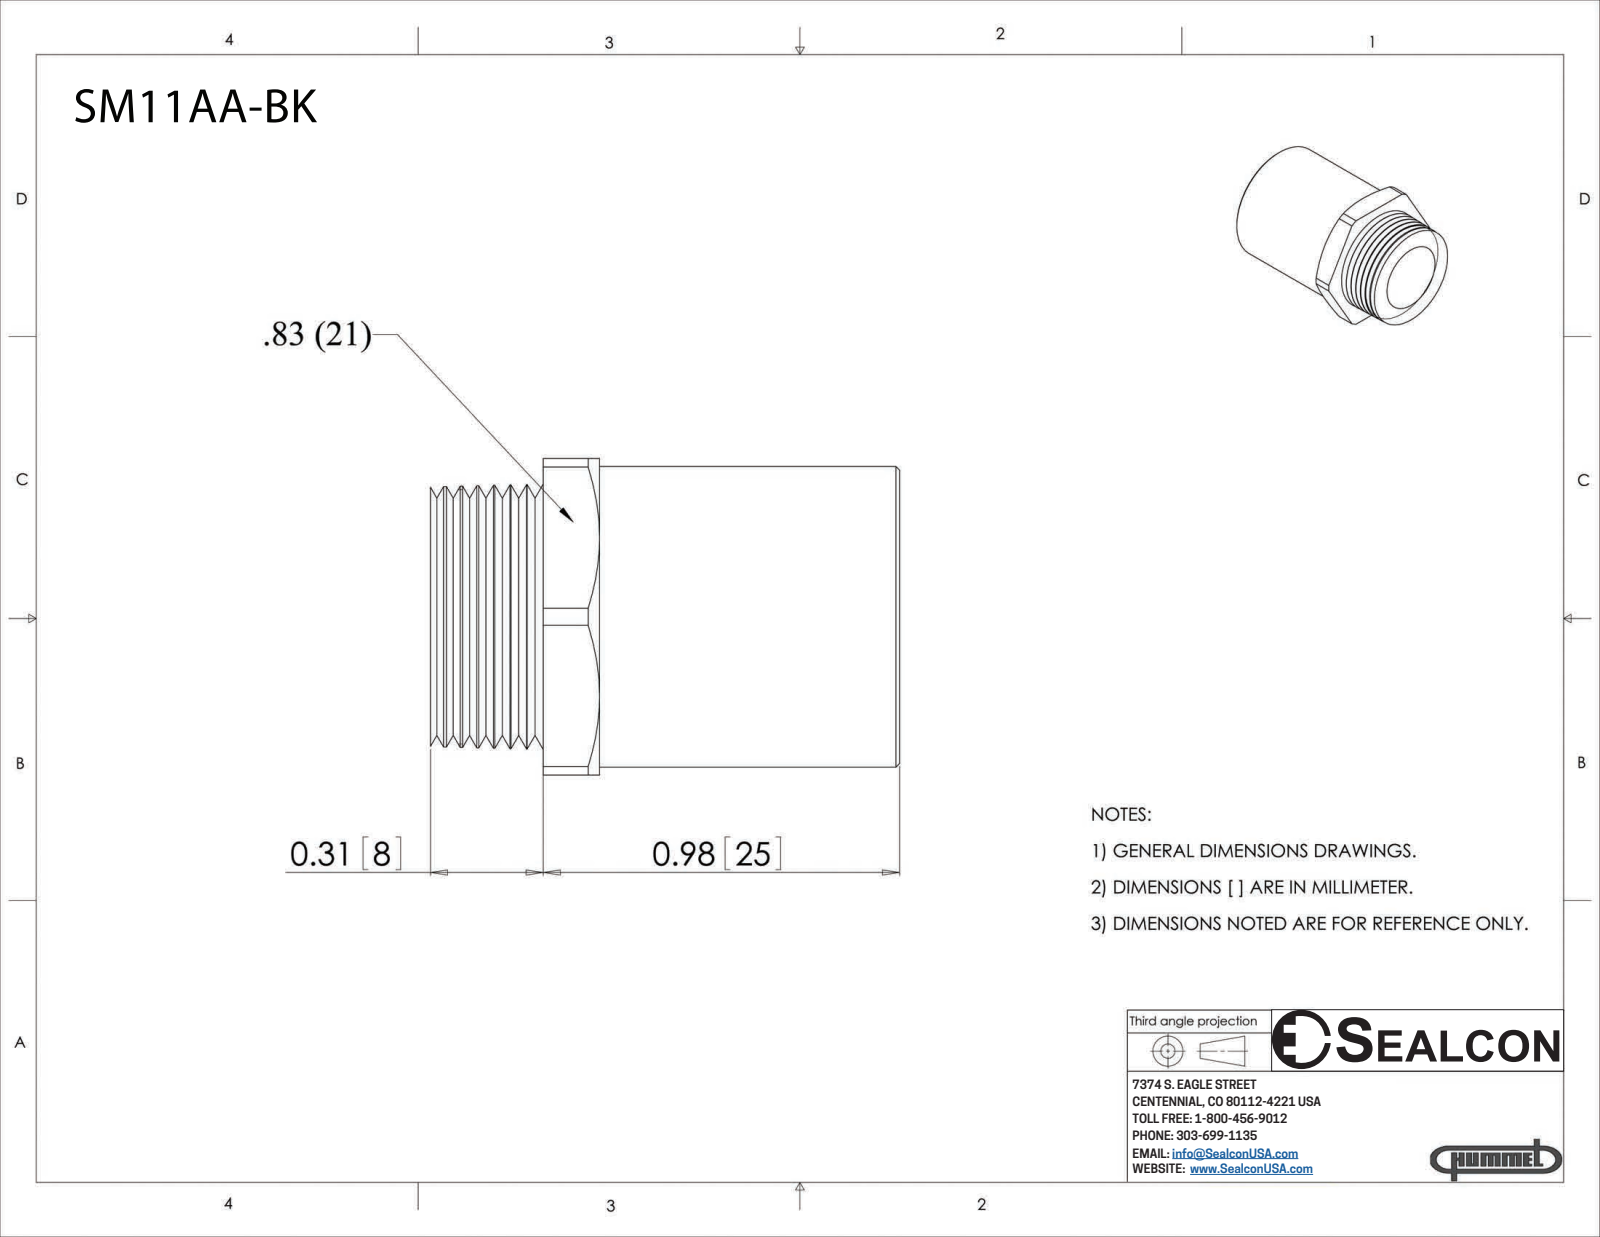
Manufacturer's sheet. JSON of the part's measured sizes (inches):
{"part_name": "SM11AA-BK", "step_written_by": "SolidWorks 2007 (AUTOMOTIVE_DESIGN)", "units": "inches", "bodies": {"solids": 1, "faces": 73, "planar": 11, "cylindrical": 11, "other": 51}, "overall_size": [1.29, 0.979, 0.87], "volume_in3": 0.245, "surface_area_in2": 7.357, "round_holes": [[0.73, 1]], "round_bosses_or_shafts": [[0.827, 1]], "partial_cylinders_radius": [[0.489, 1]], "face_to_face_distances": [0.155, 0.465, 0.31, 0.87, 0.825, 0.98, 1.29]}
